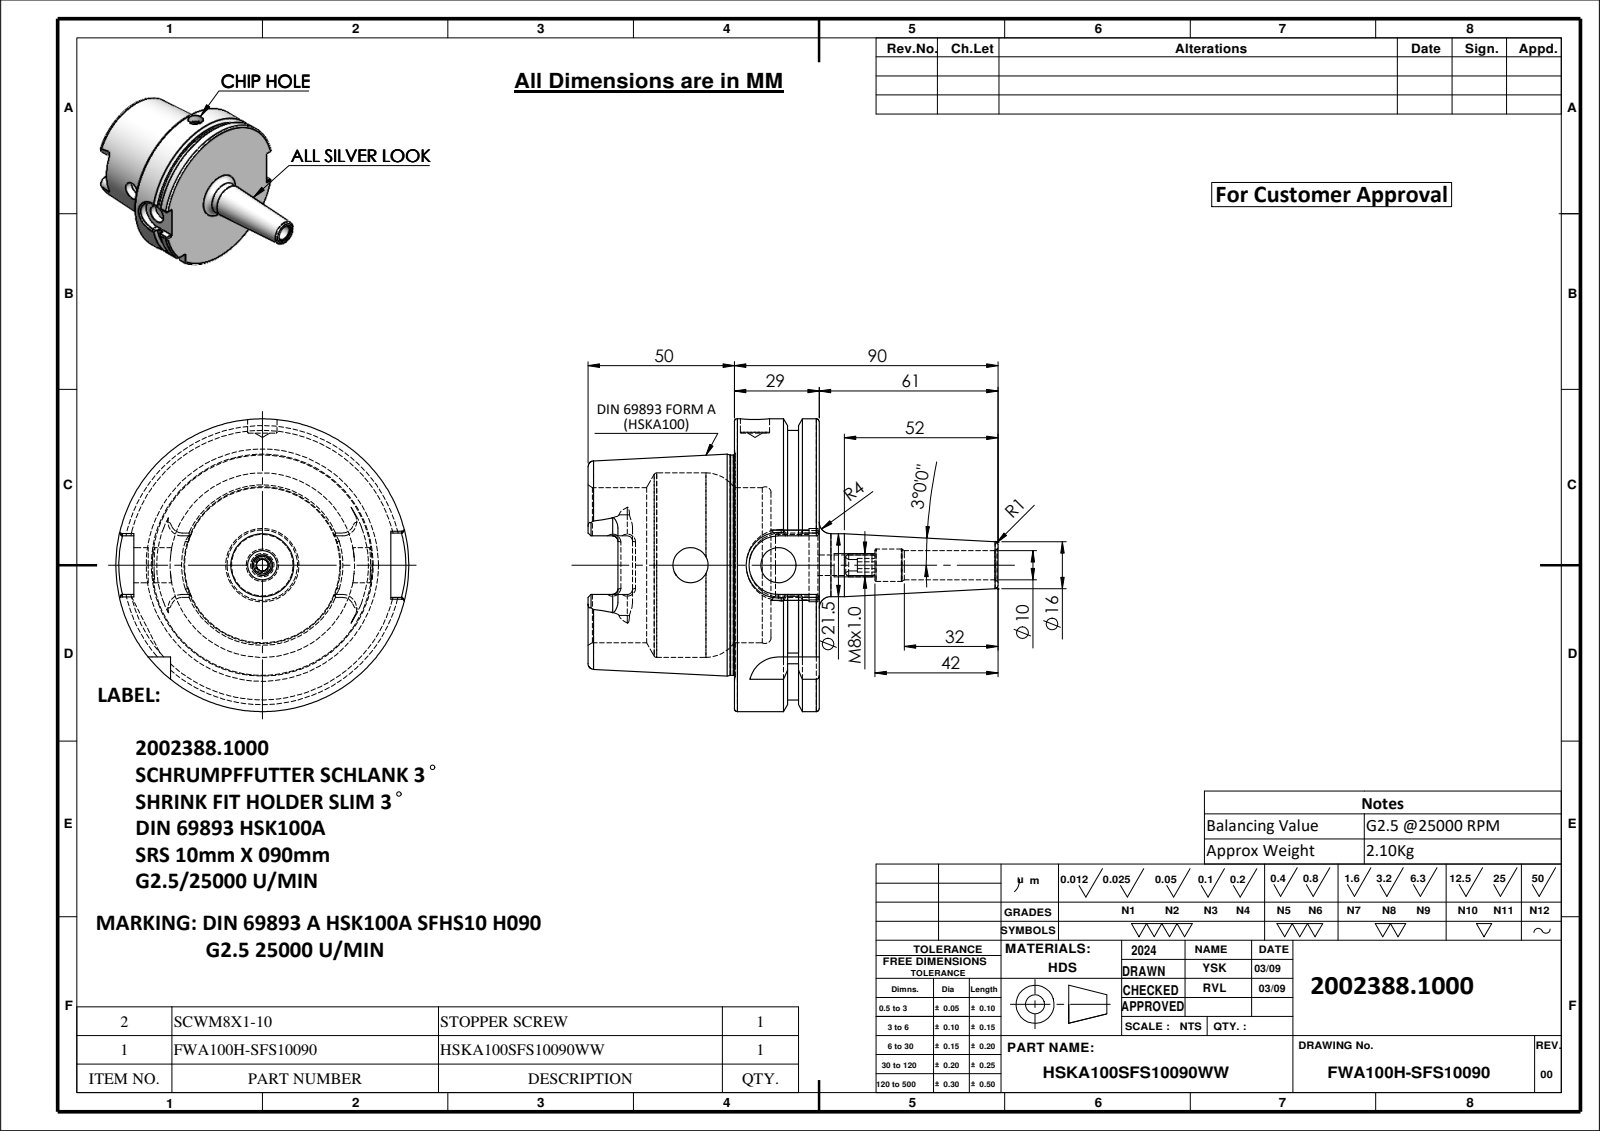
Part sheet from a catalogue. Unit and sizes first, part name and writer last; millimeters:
Units: millimetres
Overall size (bounding box): 140 × 100 × 100
Round holes (diameter × count): ⌀10 ×2, ⌀12 ×2, ⌀3.9 ×1, ⌀7 ×1, ⌀11 ×1, ⌀21 ×1, ⌀25 ×1, ⌀53 ×1, ⌀63 ×1
Round bosses / shafts (diameter × count): ⌀100 ×1, ⌀92 ×1, ⌀75.16 ×1, ⌀21.5 ×1, ⌀8 ×1
Partial cylindrical surfaces — rounded edges, fillets, slot ends (radius × count): R1.8 ×6, R4.88 ×4, R10 ×2, R11 ×1
Main face-to-face distances: 28.95, 12.5, 16.45, 50, 62.5, 78.95, 78.5, 28.5, 16, 0.45
Hole centre spacings: 30
Volume: 267 734 mm³ · Surface area: 55 403 mm²
Bodies: 2 solids, 201 faces (61 planar, 56 cylindrical, 84 other)
Part name (STEP PRODUCT): HSKA100SFS10090WW; SCWM8X1-10; FWA100H-SFS10090
STEP written by: SolidWorks 2024 (CONFIG_CONTROL_DESIGN)
